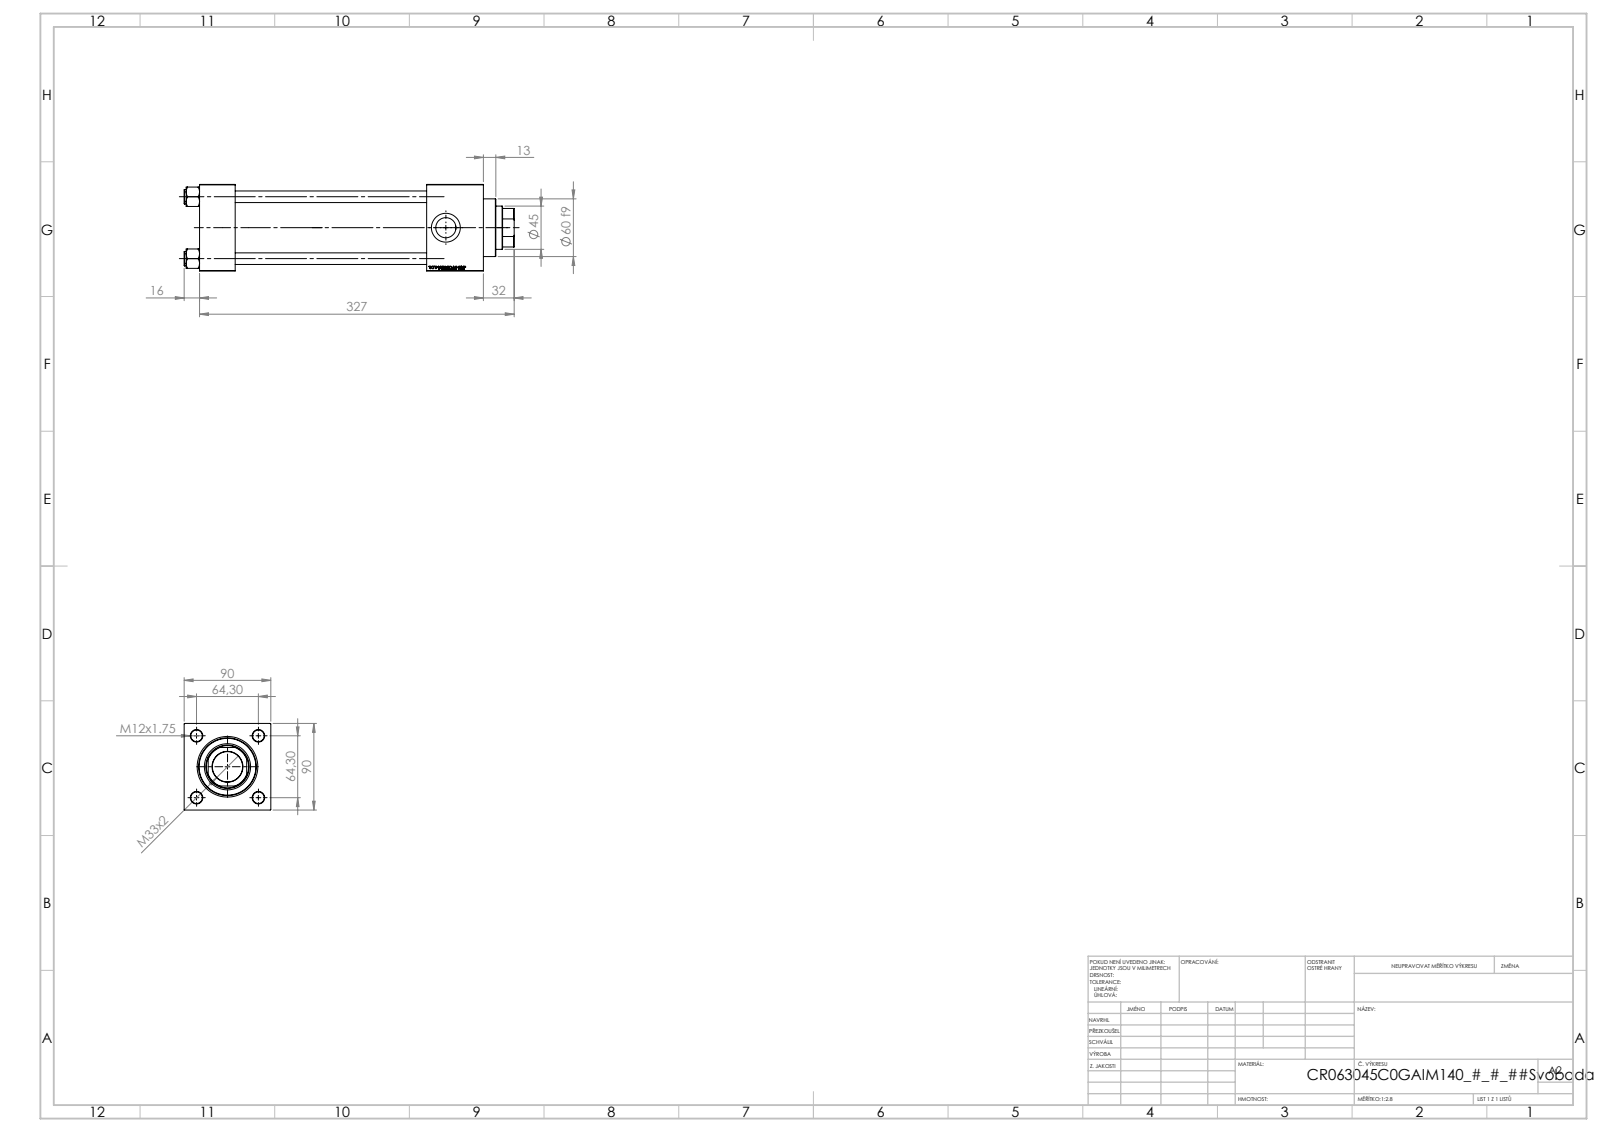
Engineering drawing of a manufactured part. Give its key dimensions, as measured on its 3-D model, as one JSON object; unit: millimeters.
{"part_name": "NUT_M5_C; V215CR_VCP_C; V215CR_C_TYCINKA; V215_VC_A (+1 more)", "step_written_by": "SolidWorks 2019 (CONFIG_CONTROL_DESIGN)", "units": "millimeters", "bodies": {"solids": 11, "faces": 1146, "planar": 525, "cylindrical": 85, "other": 536}, "overall_size": [343, 90, 90], "volume_mm3": 1371000, "surface_area_mm2": 288896, "round_holes": [[12, 4], [7, 2], [20.96, 2], [30, 2], [31.5, 1], [45, 1], [48, 1], [50, 1], [60, 1], [63, 1]], "round_bosses_or_shafts": [[15, 4], [69, 1]], "partial_cylinders_radius": [[22, 1]], "face_to_face_distances": [90, 37, 59, 236, 199, 295, 258, 266.3, 229.3, 30.3], "hole_center_spacings": [45.47, 64.3, 90.93]}
